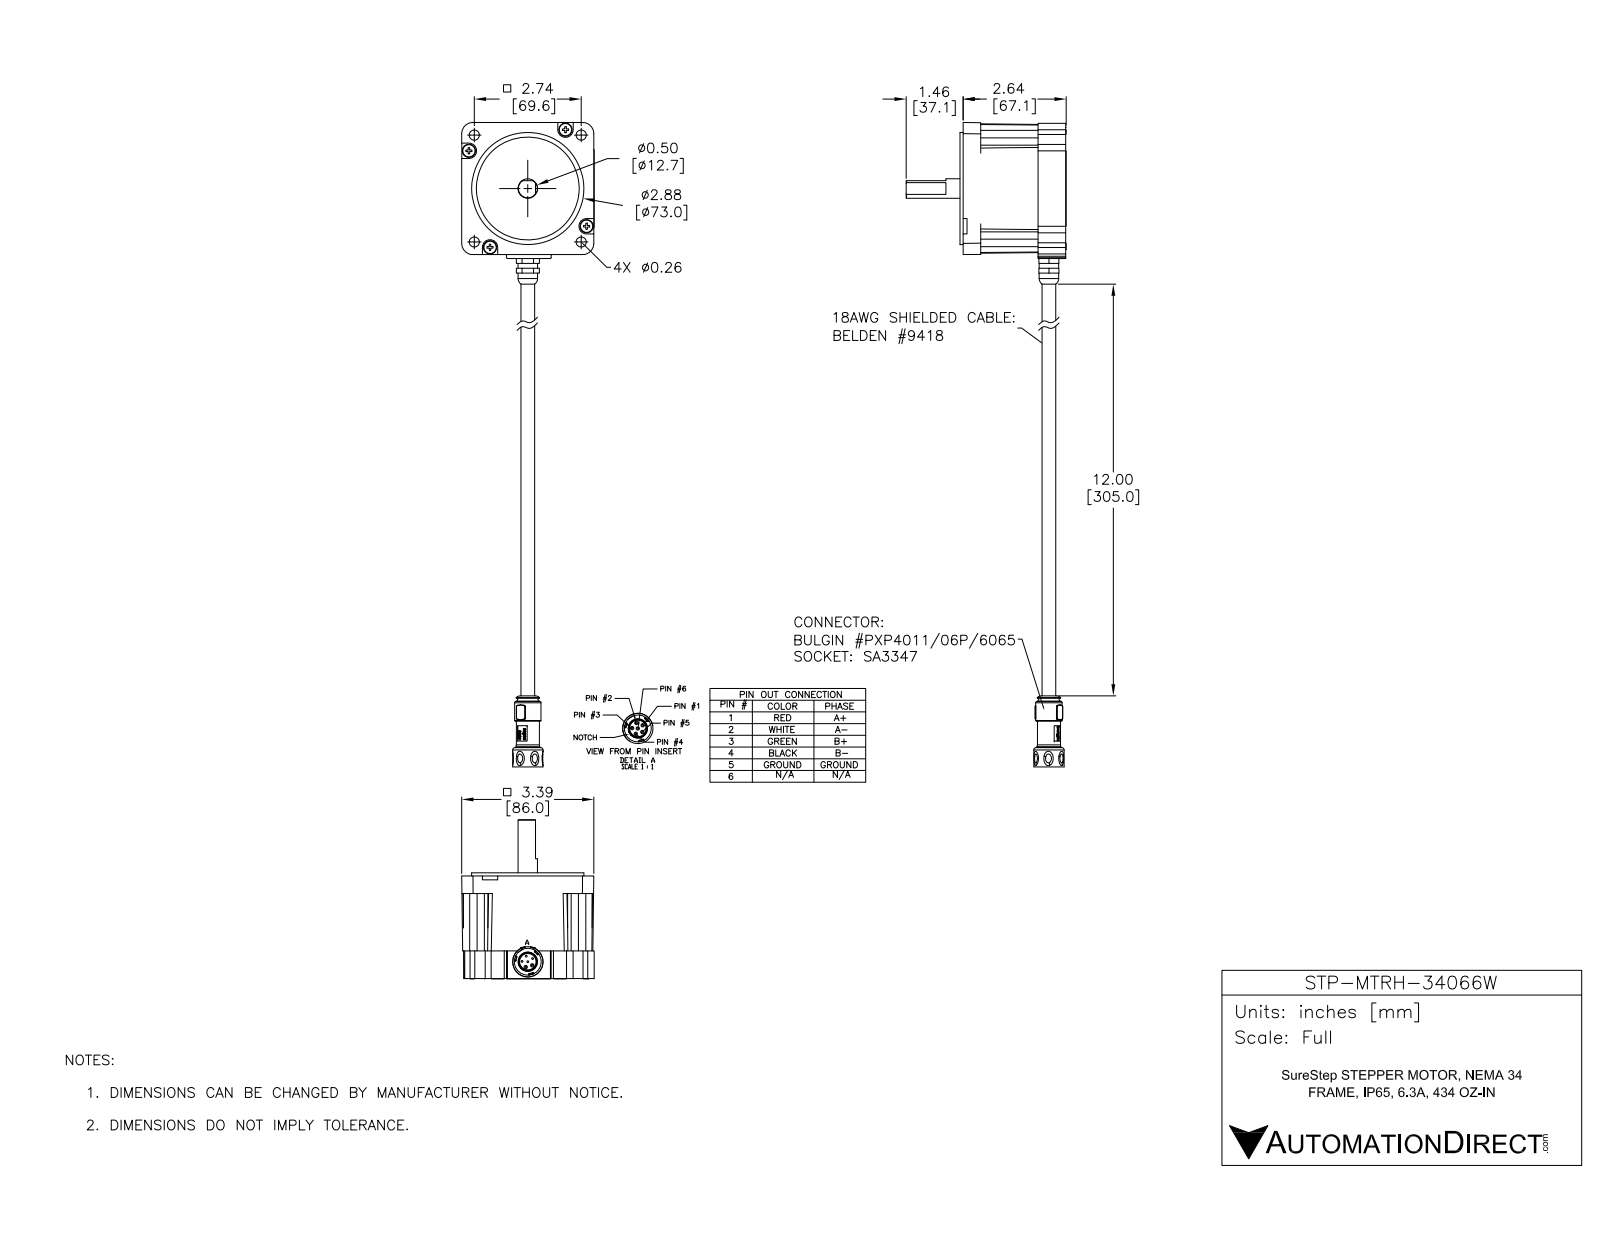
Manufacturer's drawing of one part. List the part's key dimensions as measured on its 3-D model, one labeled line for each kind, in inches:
Part name (STEP PRODUCT): STP-MTRH-34066W
STEP written by: SolidWorks 2017 (AUTOMOTIVE_DESIGN)
Units: inches
Bodies: 3 solids, 837 faces (308 planar, 234 cylindrical, 295 other)
Overall size (bounding box): 16.516 × 4.08 × 3.386
Volume: 29.04 in³ · Surface area: 83.68 in²
Round holes (diameter × count): ⌀0.047 ×6, ⌀0.13 ×4, ⌀0.26 ×4, ⌀0.125 ×1, ⌀0.228 ×1, ⌀0.449 ×1, ⌀0.689 ×1, ⌀0.75 ×1, ⌀2.638 ×1
Round bosses / shafts (diameter × count): ⌀0.05 ×4, ⌀0.5 ×2, ⌀3.125 ×1, ⌀2.875 ×1, ⌀0.777 ×1, ⌀0.674 ×1, ⌀0.613 ×1, ⌀0.592 ×1
Partial cylindrical surfaces — rounded edges, fillets, slot ends (radius × count): R0.005 ×28, R0.008 ×16, R0.02 ×14, R0.188 ×8, R0.388 ×6, R0.187 ×4, R0.197 ×4, R0.287 ×3
Main face-to-face distances: 2.68, 0.04, 2.64, 2.63, 2.67, 3.346, 2.222, 2.21, 2.2, 0.43
Hole centre spacings: 0.148, 0.174, 0.147, 1.937, 2.533, 2.74, 0.281, 3.707
